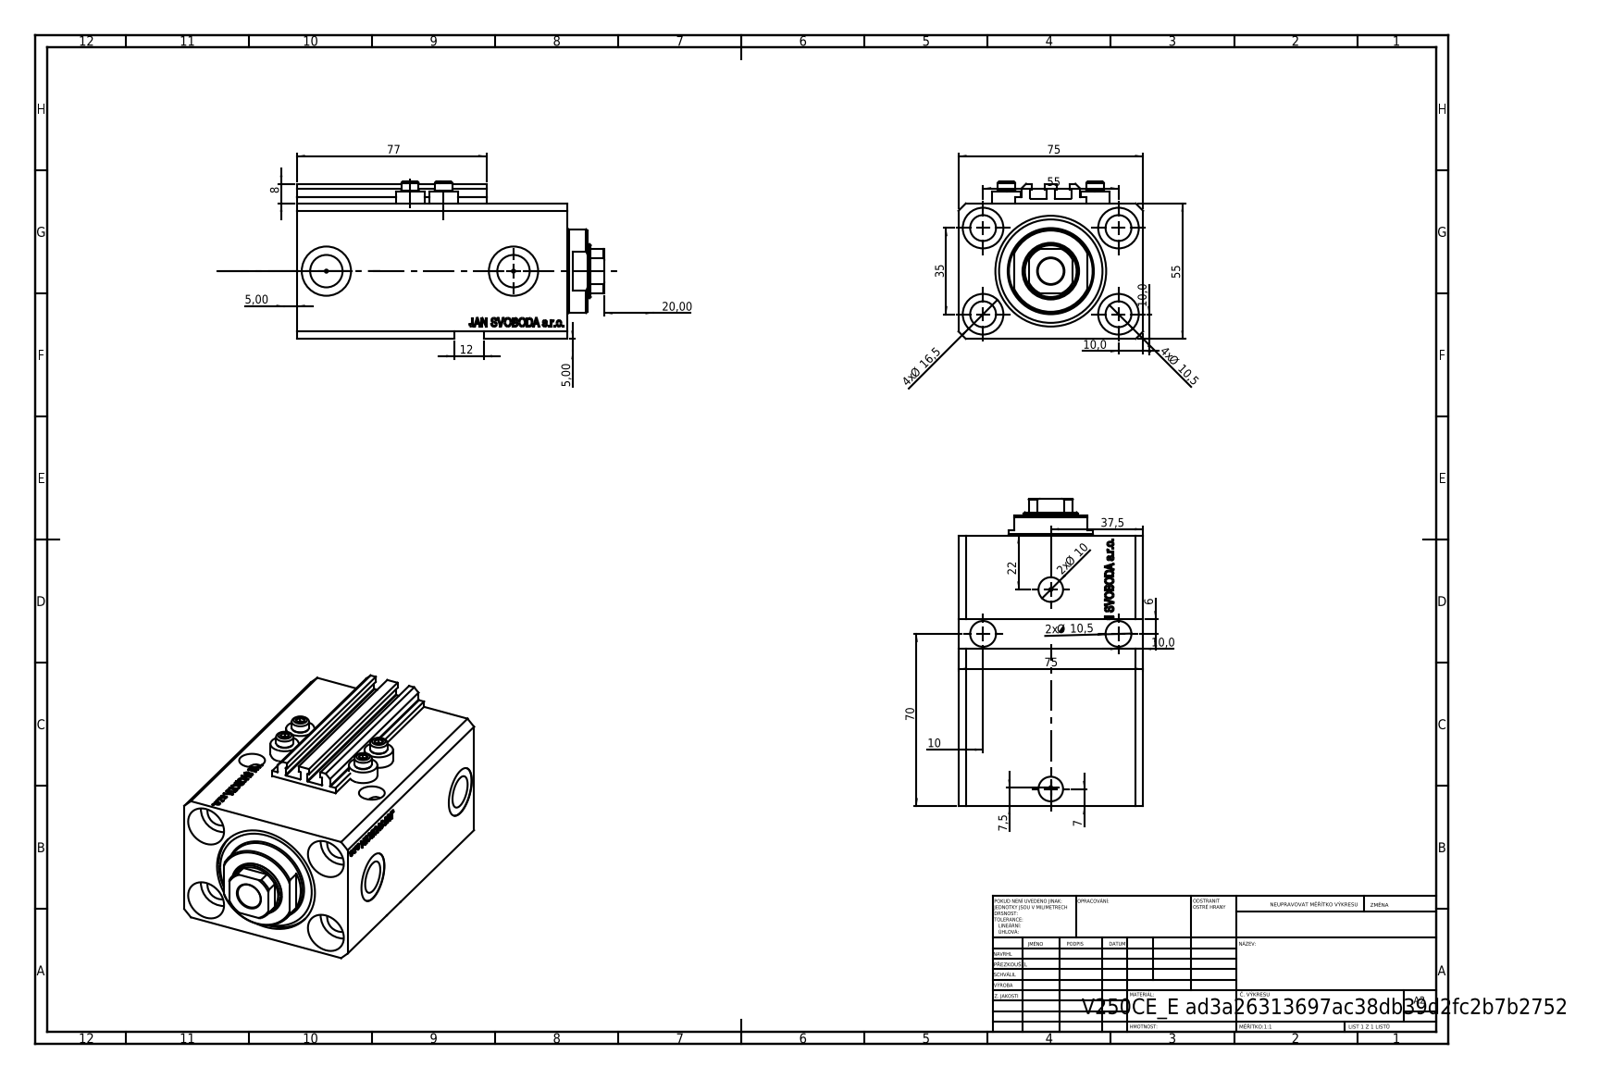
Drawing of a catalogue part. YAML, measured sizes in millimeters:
part_name: "V250CE_E; V250CE_VC_E; V250CE_C_VCP; ALLEN BOLT V250CE"
step_written_by: "SolidWorks 2019 (CONFIG_CONTROL_DESIGN)"
units: millimeters
bodies: {solids: 8, faces: 1080, planar: 518, cylindrical: 138, other: 424}
overall_size: [124.9, 75, 64]
volume: 384142
surface_area: 97850
round_holes:
  - {diameter: 10.5, count: 7}
  - {diameter: 1.25, count: 4}
  - {diameter: 4, count: 4}
  - {diameter: 16.5, count: 4}
  - {diameter: 10, count: 2}
  - {diameter: 13.16, count: 2}
  - {diameter: 20, count: 2}
  - {diameter: 22, count: 1}
  - {diameter: 32, count: 1}
  - {diameter: 45, count: 1}
round_bosses_or_shafts:
  - {diameter: 11.6, count: 4}
  - {diameter: 7, count: 4}
  - {diameter: 34, count: 1}
partial_cylinders:
  - {radius: 0.2, count: 10}
  - {radius: 10.5, count: 1}
face_to_face_distances: [55, 75, 110, 82.9, 27.1, 9.9, 3, 73, 100.1, 57]
hole_center_spacings: [32.6, 55, 13.6, 14.09, 25.81, 32.87, 33.62, 35]
